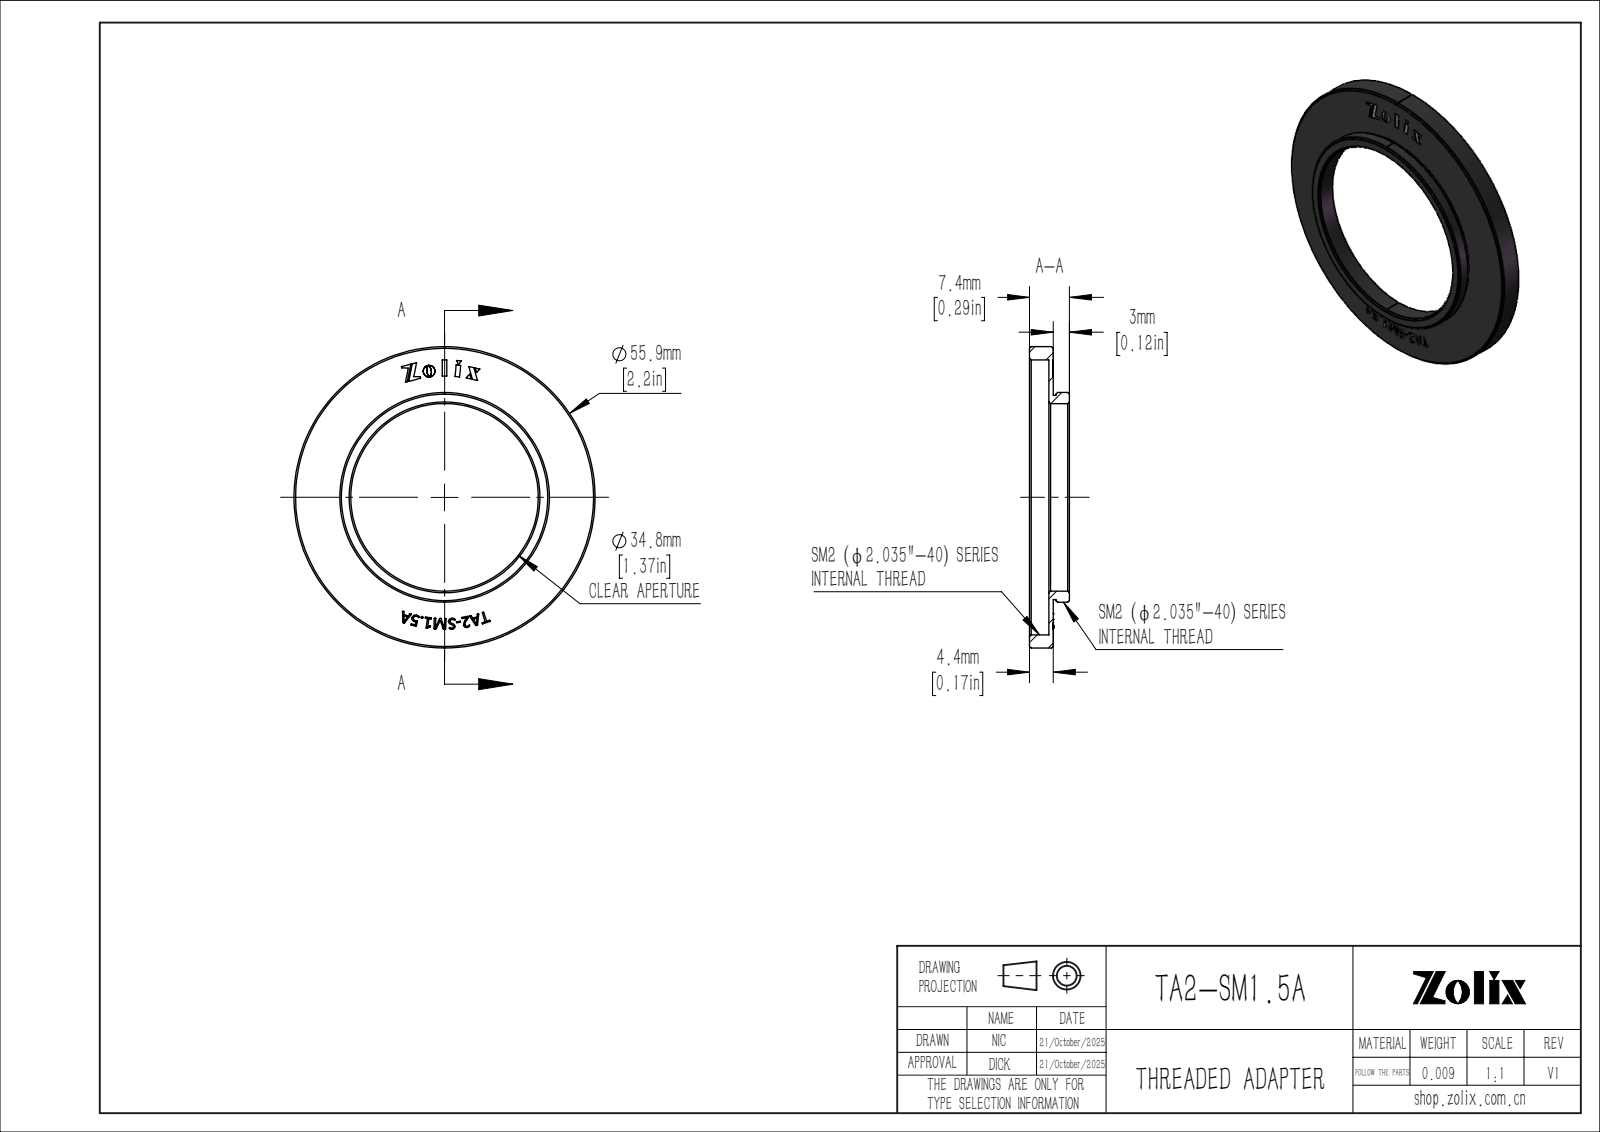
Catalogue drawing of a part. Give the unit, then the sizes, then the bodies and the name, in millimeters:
Units: millimetres
Overall size (bounding box): 55.9 × 55.9 × 7.4
Round holes (diameter × count): ⌀34.8 ×1, ⌀51 ×1
Round bosses / shafts (diameter × count): ⌀55.9 ×1, ⌀38.9 ×1, ⌀37.89 ×1
Main face-to-face distances: 0.8, 3.6, 4.4, 3, 7.4, 3.8, 4.9, 1.3, 0.5, 2.5
Volume: 3 321 mm³ · Surface area: 5 089 mm²
Bodies: 1 solid, 342 faces (226 planar, 10 cylindrical, 106 other)
Part name (STEP PRODUCT): TA2-SM1.5A
STEP written by: SolidWorks 2020 (CONFIG_CONTROL_DESIGN)
